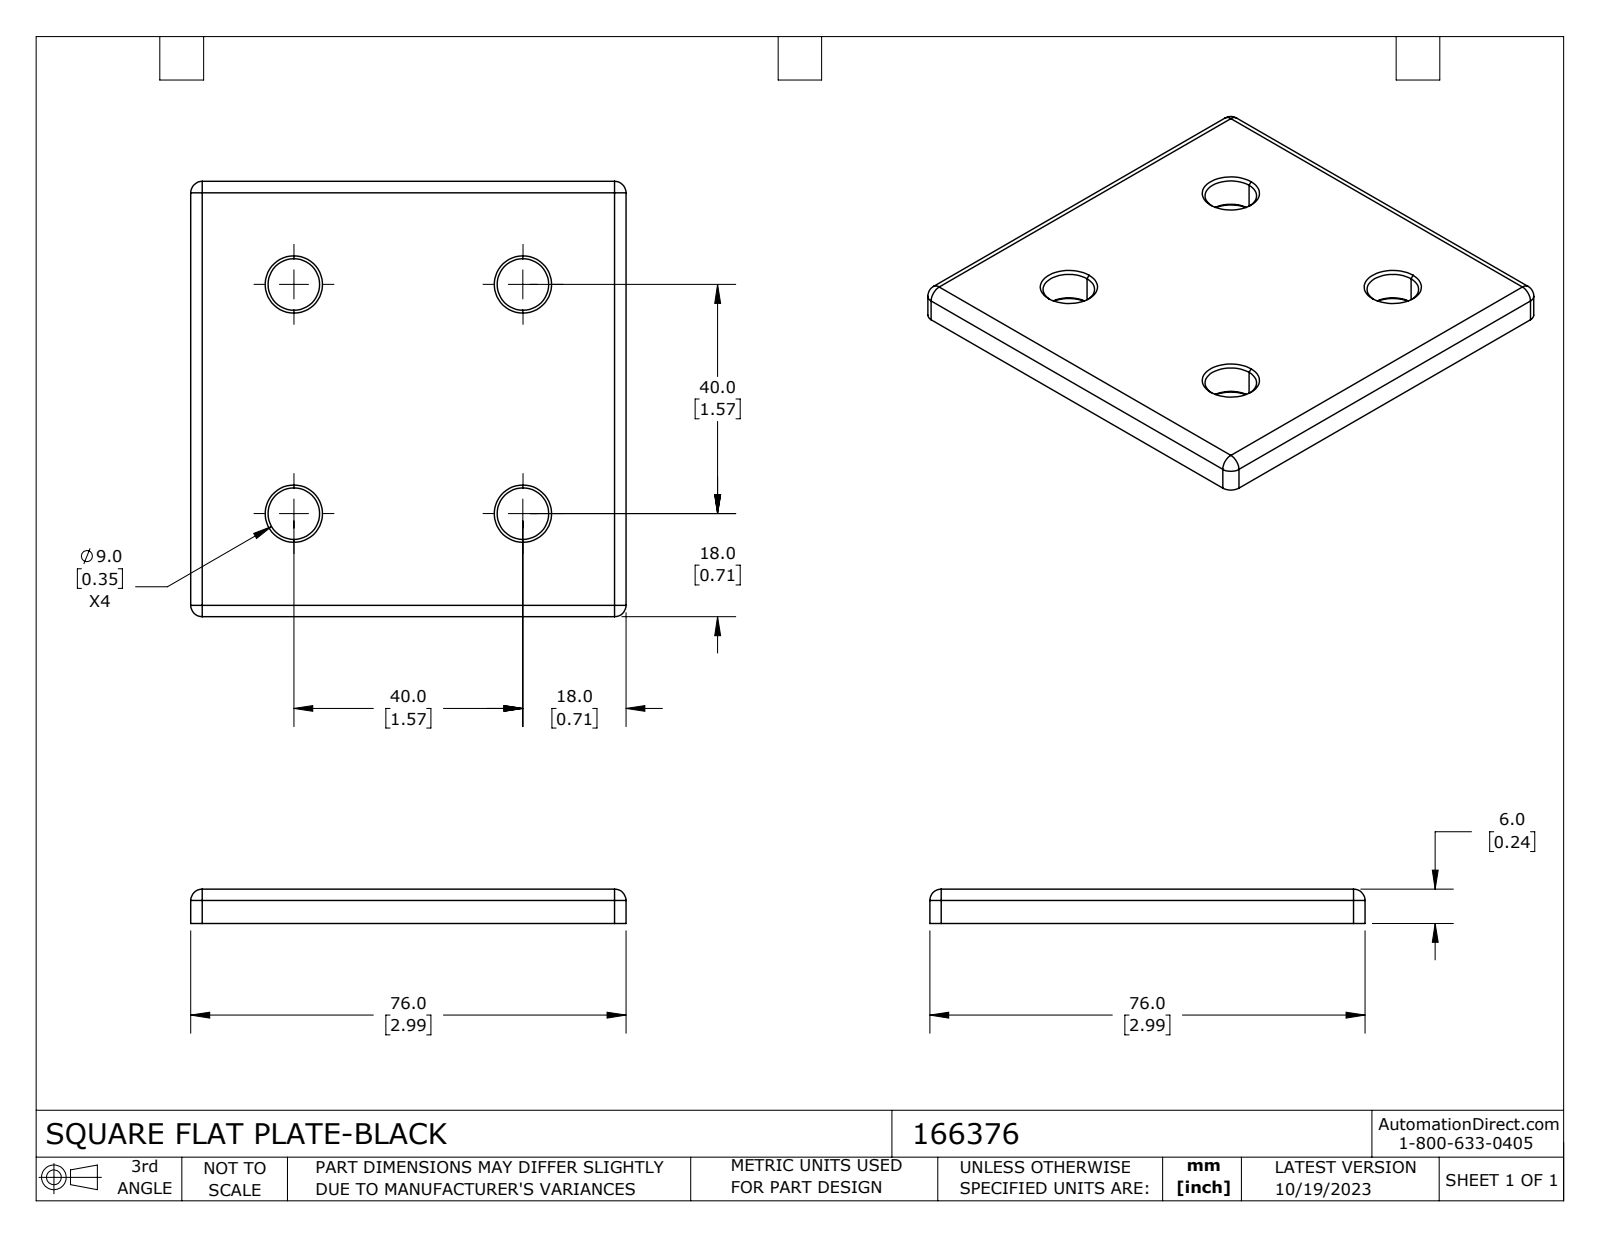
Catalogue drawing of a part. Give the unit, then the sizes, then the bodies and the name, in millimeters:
Units: millimetres
Overall size (bounding box): 76 × 76 × 6
Round holes (diameter × count): ⌀9 ×4
Partial cylindrical surfaces — rounded edges, fillets, slot ends (radius × count): R2 ×8
Main face-to-face distances: 6, 76
Hole centre spacings: 40, 56.57
Volume: 32 824 mm³ · Surface area: 13 195 mm²
Bodies: 1 solid, 42 faces (6 planar, 16 cylindrical, 20 other)
Part name (STEP PRODUCT): 166376
STEP written by: SolidWorks 2023 (CONFIG_CONTROL_DESIGN)
